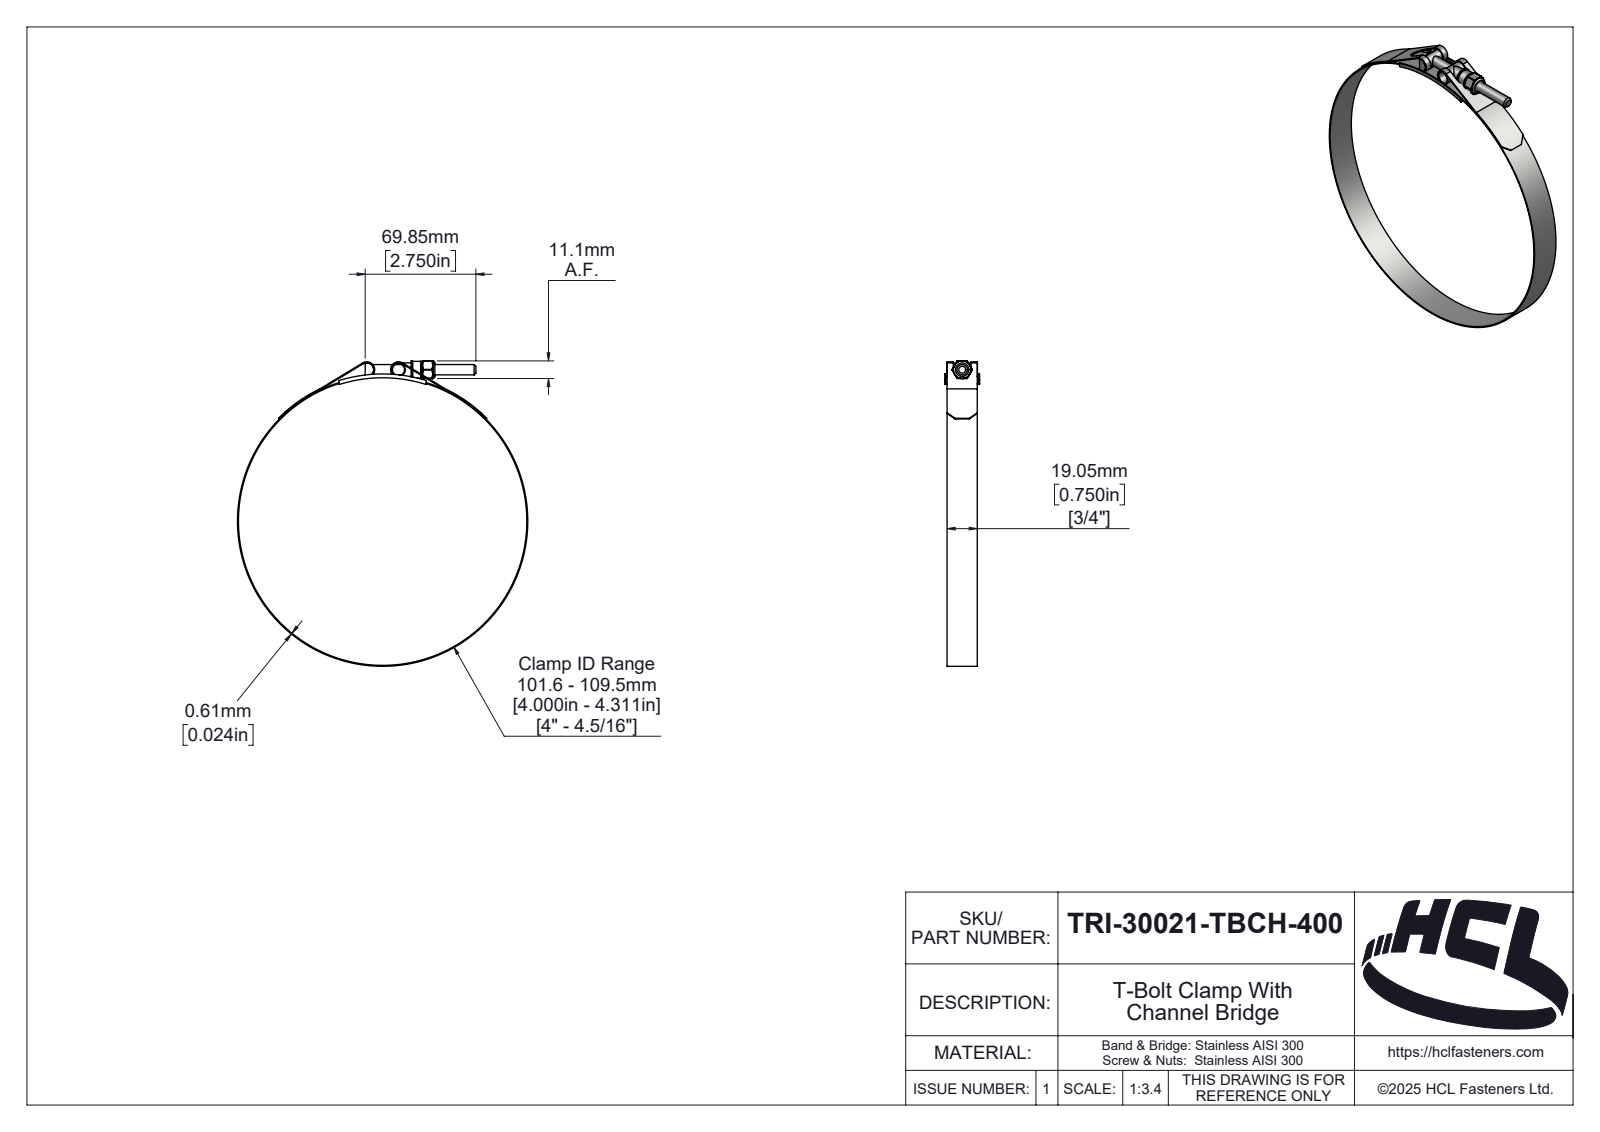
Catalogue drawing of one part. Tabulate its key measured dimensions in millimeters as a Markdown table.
| quantity | value |
| --- | --- |
| part name | TRI-30021-TBCH-400 |
| STEP written by | SolidWorks 2025 (AUTOMOTIVE_DESIGN) |
| units | millimeters |
| bodies | 6 solids, 330 faces (46 planar, 122 cylindrical, 162 other) |
| overall size | 192.81 × 183.22 × 22 |
| volume | 12 949 mm³ |
| surface area | 34 151 mm² |
| round holes (diameter × count) | 5.4 × 1, 6.35 × 1, 6.5 × 1, 7.58 × 1, 182 × 1 |
| round bosses / shafts (diameter × count) | 8.58 × 2, 183.22 × 1, 10.58 × 1 |
| partial cylindrical surfaces (radius × count) | 0.39 × 6, 0.5 × 2, 4.39 × 2, 5 × 2, 0.59 × 1, 2.42 × 1, 3.03 × 1, 3.19 × 1 |
| main face-to-face distances | 0.6, 19.06, 1.47, 20.53, 0.61, 21.39, 0.86, 19.92, 0.74, 22 |
| hole center spacings | 96 |
